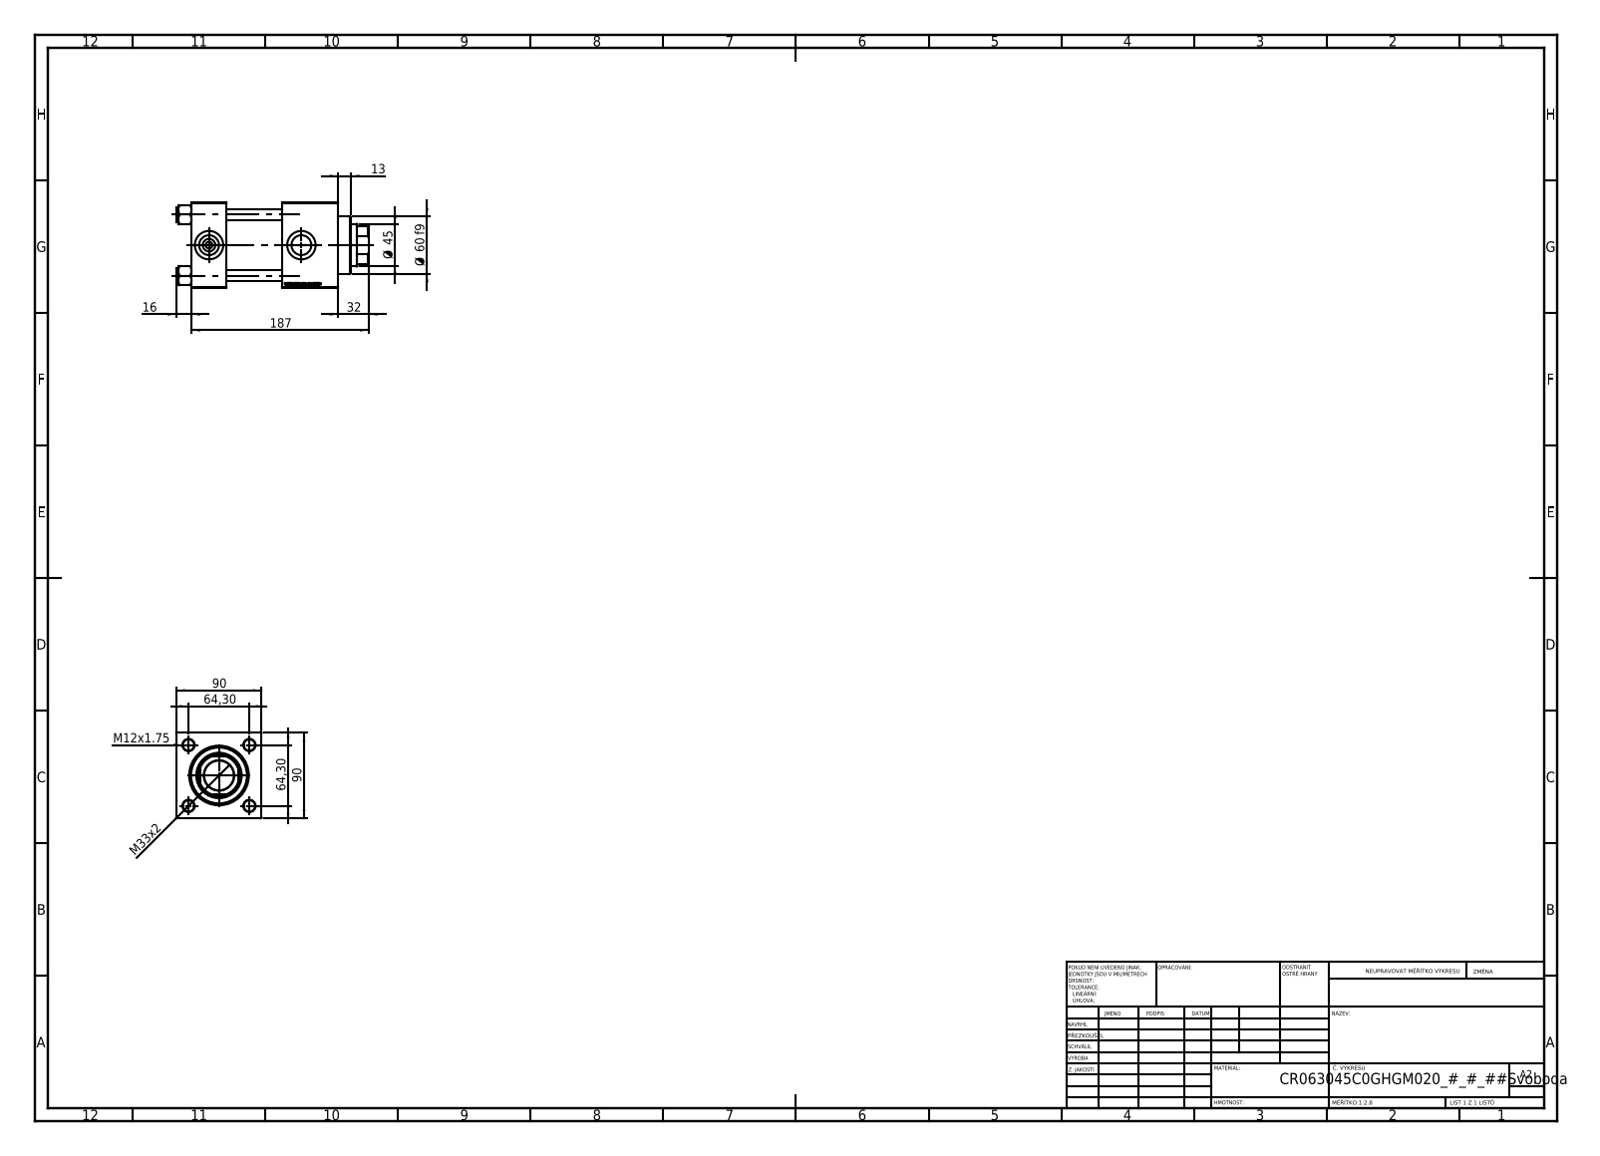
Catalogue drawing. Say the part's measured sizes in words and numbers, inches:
The part is named "NUT_M5_C; V215CR_VCP_C; V215_VC_A; V215CR_C_TYCINKA (+1 more)". Its 3-D file was written by "SolidWorks 2019 (CONFIG_CONTROL_DESIGN)". It is 11 solids with 1145 faces: 525 planar, 84 cylindrical and 536 other. Overall it measures 7.992 by 3.543 by 3.543 inches. Its volume is 60.9 cubic inches and its surface area 294.4 square inches. Round holes: 4 of diameter 0.472, 2 of diameter 0.276, 2 of diameter 0.825, 2 of diameter 1.181, 1 of diameter 1.24, 1 of diameter 1.772, 1 of diameter 1.89, 1 of diameter 1.969, 1 of diameter 2.362, 1 of diameter 2.48. Round bosses or shafts: 4 of diameter 0.591, 1 of diameter 2.717. Partial cylindrical surfaces (rounded edges, fillets, slot ends): 1 of radius 0.866. The main face-to-face distances are 3.543, 2.323, 1.457, 3.78, 6.102, 4.646, 4.972, 3.516, 1.193, 1.13. The hole center spacings are 1.79, 2.531, 3.58, 3.839.
